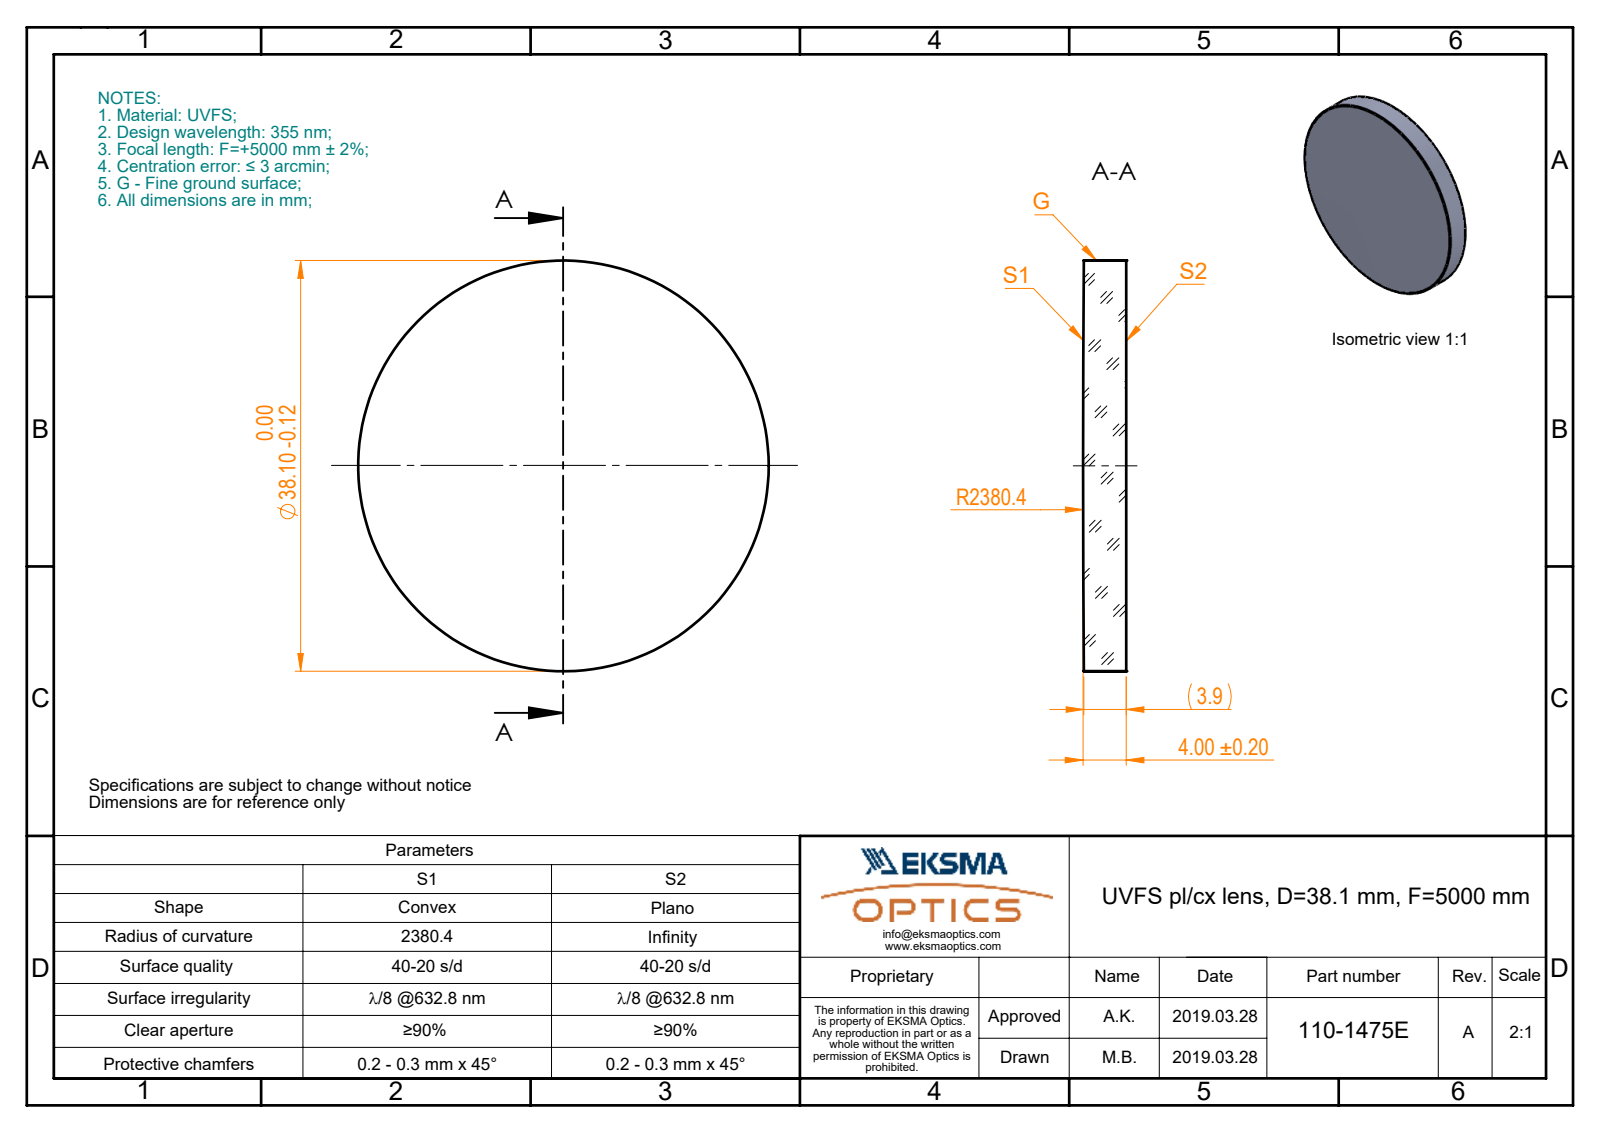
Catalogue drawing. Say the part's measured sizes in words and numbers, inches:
The part is named "110-1475E UVFS pl-cx 38.1 F5000". Its 3-D file was written by "SolidWorks 2017 (CONFIG_CONTROL_DESIGN)". It is 1 solid with 5 faces: 1 planar, 2 cylindrical and 2 other. Overall it measures 1.5 by 1.5 by 0.157 inches. Its volume is 0.276 cubic inches and its surface area 4.263 square inches. Round bosses or shafts: 1 of diameter 1.5.
